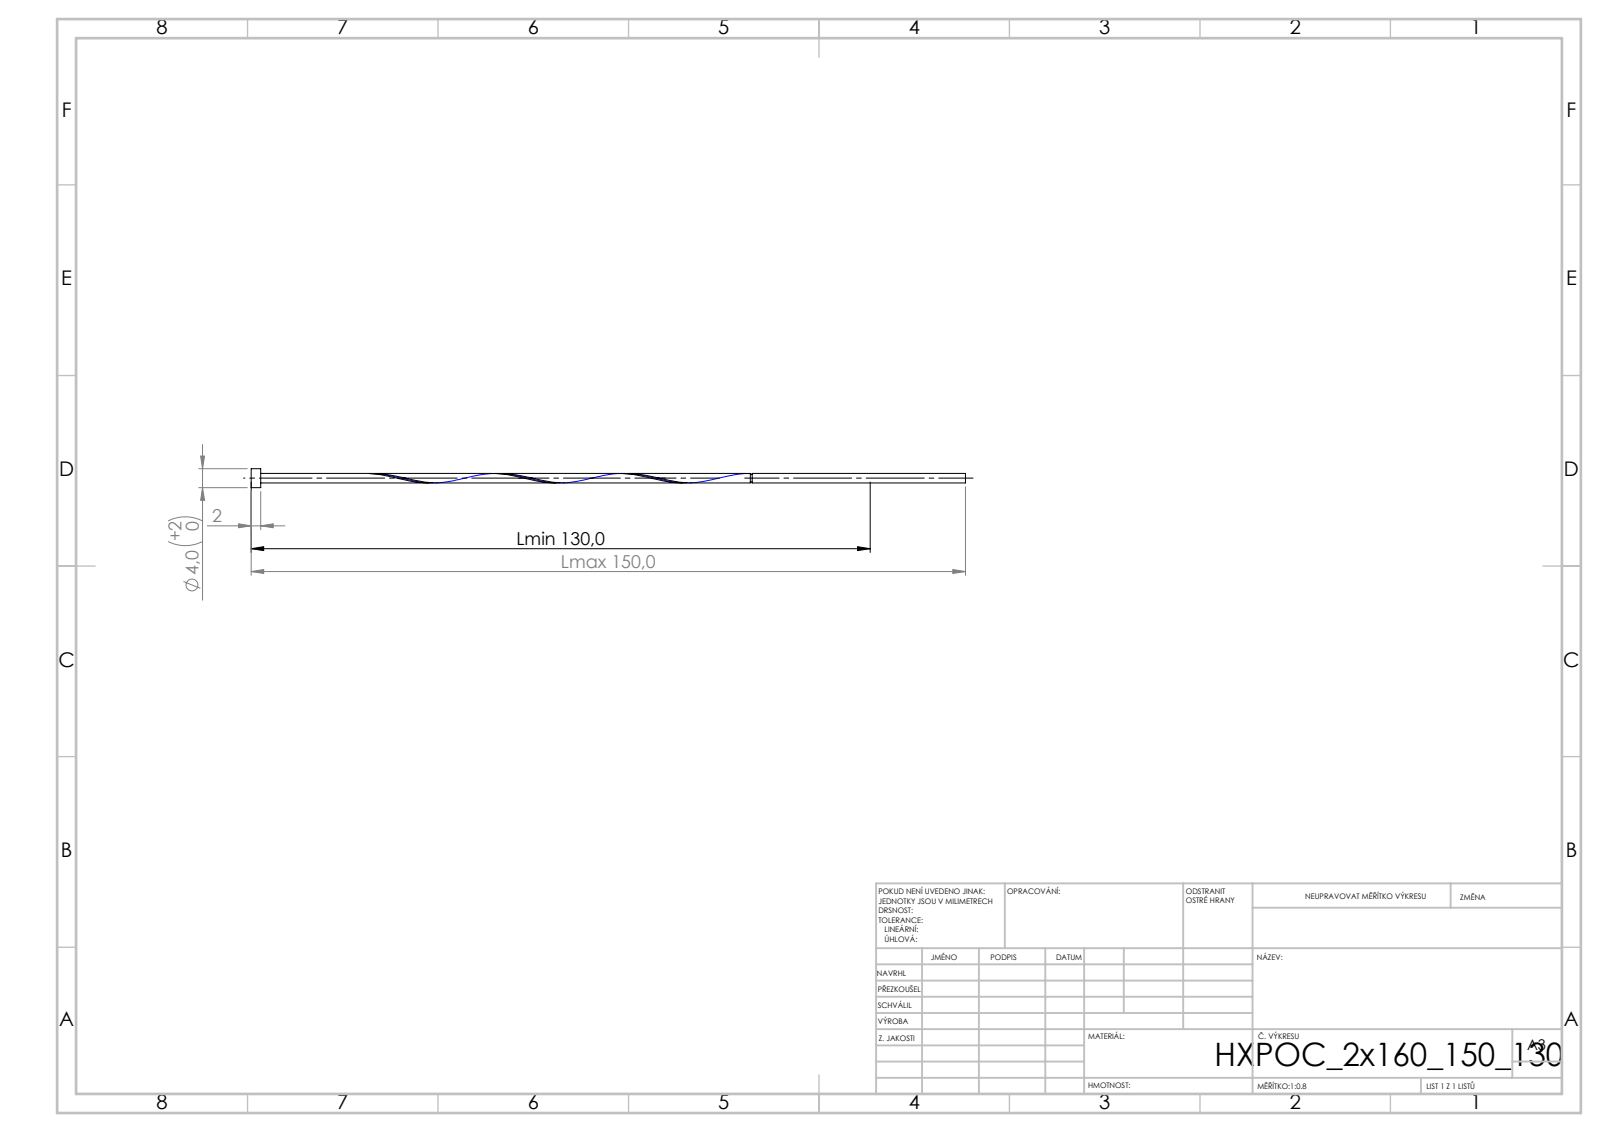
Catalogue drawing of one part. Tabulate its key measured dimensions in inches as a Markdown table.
| quantity | value |
| --- | --- |
| STEP written by | SolidWorks 2019 (CONFIG_CONTROL_DESIGN) |
| units | inches |
| bodies | 1 solid, 16 faces (6 planar, 9 cylindrical, 1 other) |
| overall size | 5.906 × 0.157 × 0.157 |
| volume | 0.036 in³ |
| surface area | 2.065 in² |
| round bosses / shafts (diameter × count) | 0.157 × 1, 0.079 × 1, 0.063 × 1 |
| main face-to-face distances | 0.079, 5.906, 5.827, 4.143, 4.065, 1.762, 4.128, 4.049, 0.016, 1.778 |
